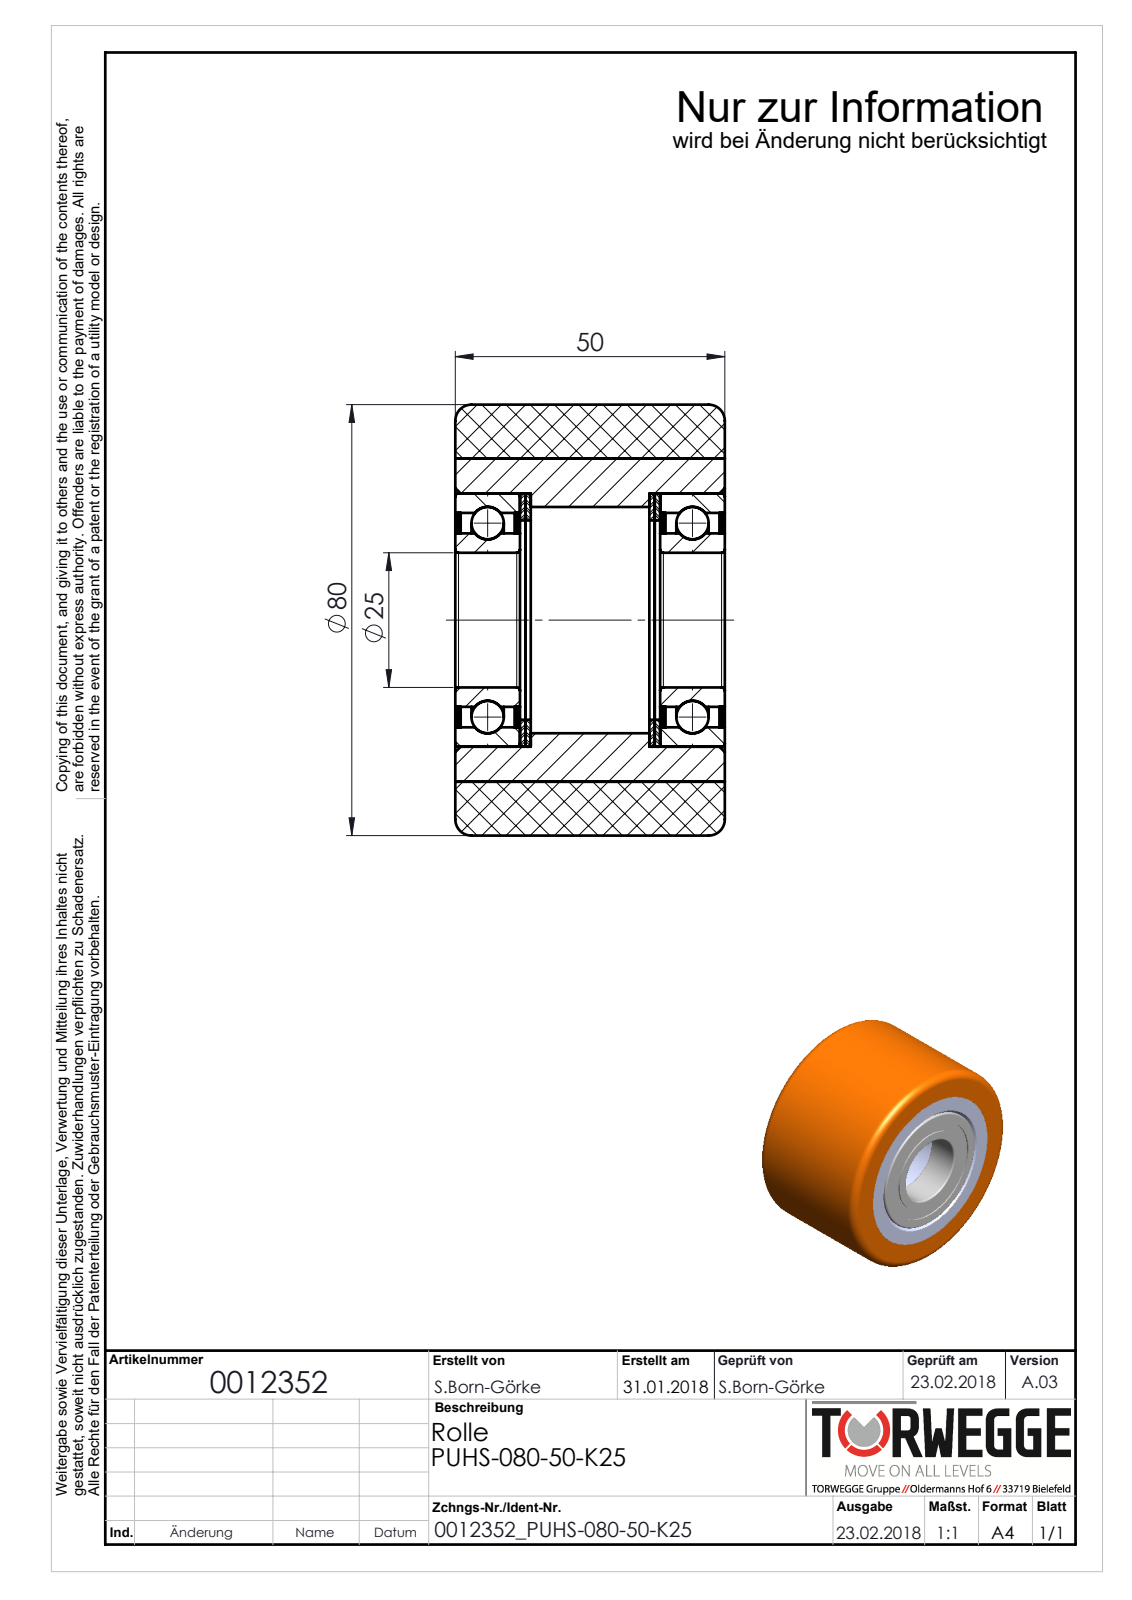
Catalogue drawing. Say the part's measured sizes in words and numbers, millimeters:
The part is named "0012352_PUHS-080-50-K25". Its 3-D file was written by "SolidWorks 2016 (AUTOMOTIVE_DESIGN)". It is 16 solids with 158 faces: 30 planar, 68 cylindrical and 60 other. Overall it measures 80 by 80 by 50 millimeters. Its volume is 198 653 cubic millimeters and its surface area 73 479 square millimeters. Round holes: 1 of diameter 25, 1 of diameter 32.2, 1 of diameter 37, 1 of diameter 39.8, 1 of diameter 42, 1 of diameter 60. Round bosses or shafts: 1 of diameter 80, 1 of diameter 47. The main face-to-face distances are 1, 38, 12, 0.5, 13, 37, 25, 24, 50, 36.
